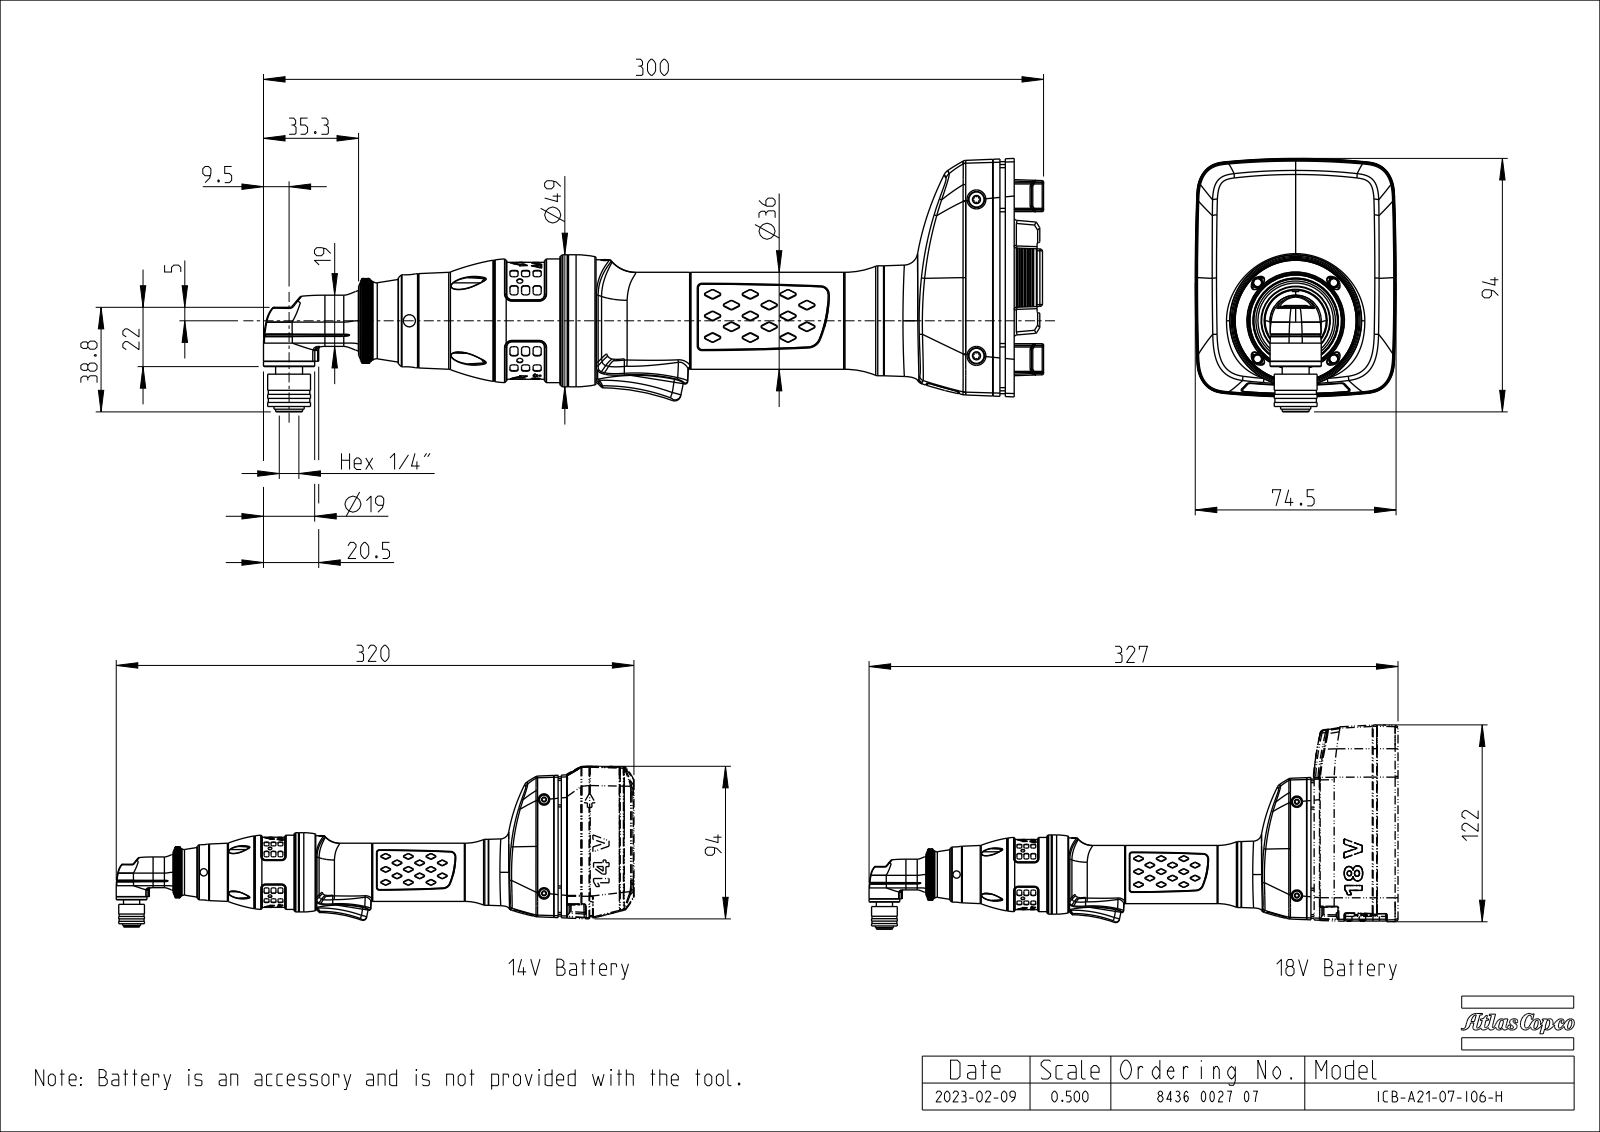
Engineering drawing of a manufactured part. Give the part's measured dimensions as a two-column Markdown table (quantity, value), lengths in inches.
| quantity | value |
| --- | --- |
| part name | EXT_COMP_SW0012 |
| STEP written by | CREO PARAMETRIC BY PTC INC, 2020281 (CONFIG_CONTROL_DESIGN) |
| units | inches |
| bodies | 7 solids, 9655 faces (6547 planar, 1051 cylindrical, 2057 other) |
| overall size | 11.402 × 3.703 × 2.935 |
| volume | 8.247 in³ |
| surface area | 120.9 in² |
| round holes (diameter × count) | 0.102 × 4, 0.177 × 2, 0.236 × 2, 0.079 × 1, 0.098 × 1, 0.114 × 1, 0.128 × 1, 0.138 × 1, 0.157 × 1, 0.197 × 1, 0.205 × 1, 0.291 × 1 |
| round bosses / shafts (diameter × count) | 0.315 × 4, 0.22 × 3, 1.929 × 1, 1.807 × 1, 1.783 × 1, 1.713 × 1, 1.709 × 1, 1.689 × 1 |
| partial cylindrical surfaces (radius × count) | 0.02 × 78, 0.039 × 62, 0.006 × 34, 0.011 × 30, 0.02 × 30, 0.012 × 26, 0.015 × 24, 0.027 × 24 |
| main face-to-face distances | 6.64, 4.744, 1.896, 4.743, 1.897, 7.524, 2.781, 2.78, 0.884, 0.118 |
| hole center spacings | 0.289, 0.409, 0.579, 0.815, 0.898, 1.469, 1.546, 1.758 |
